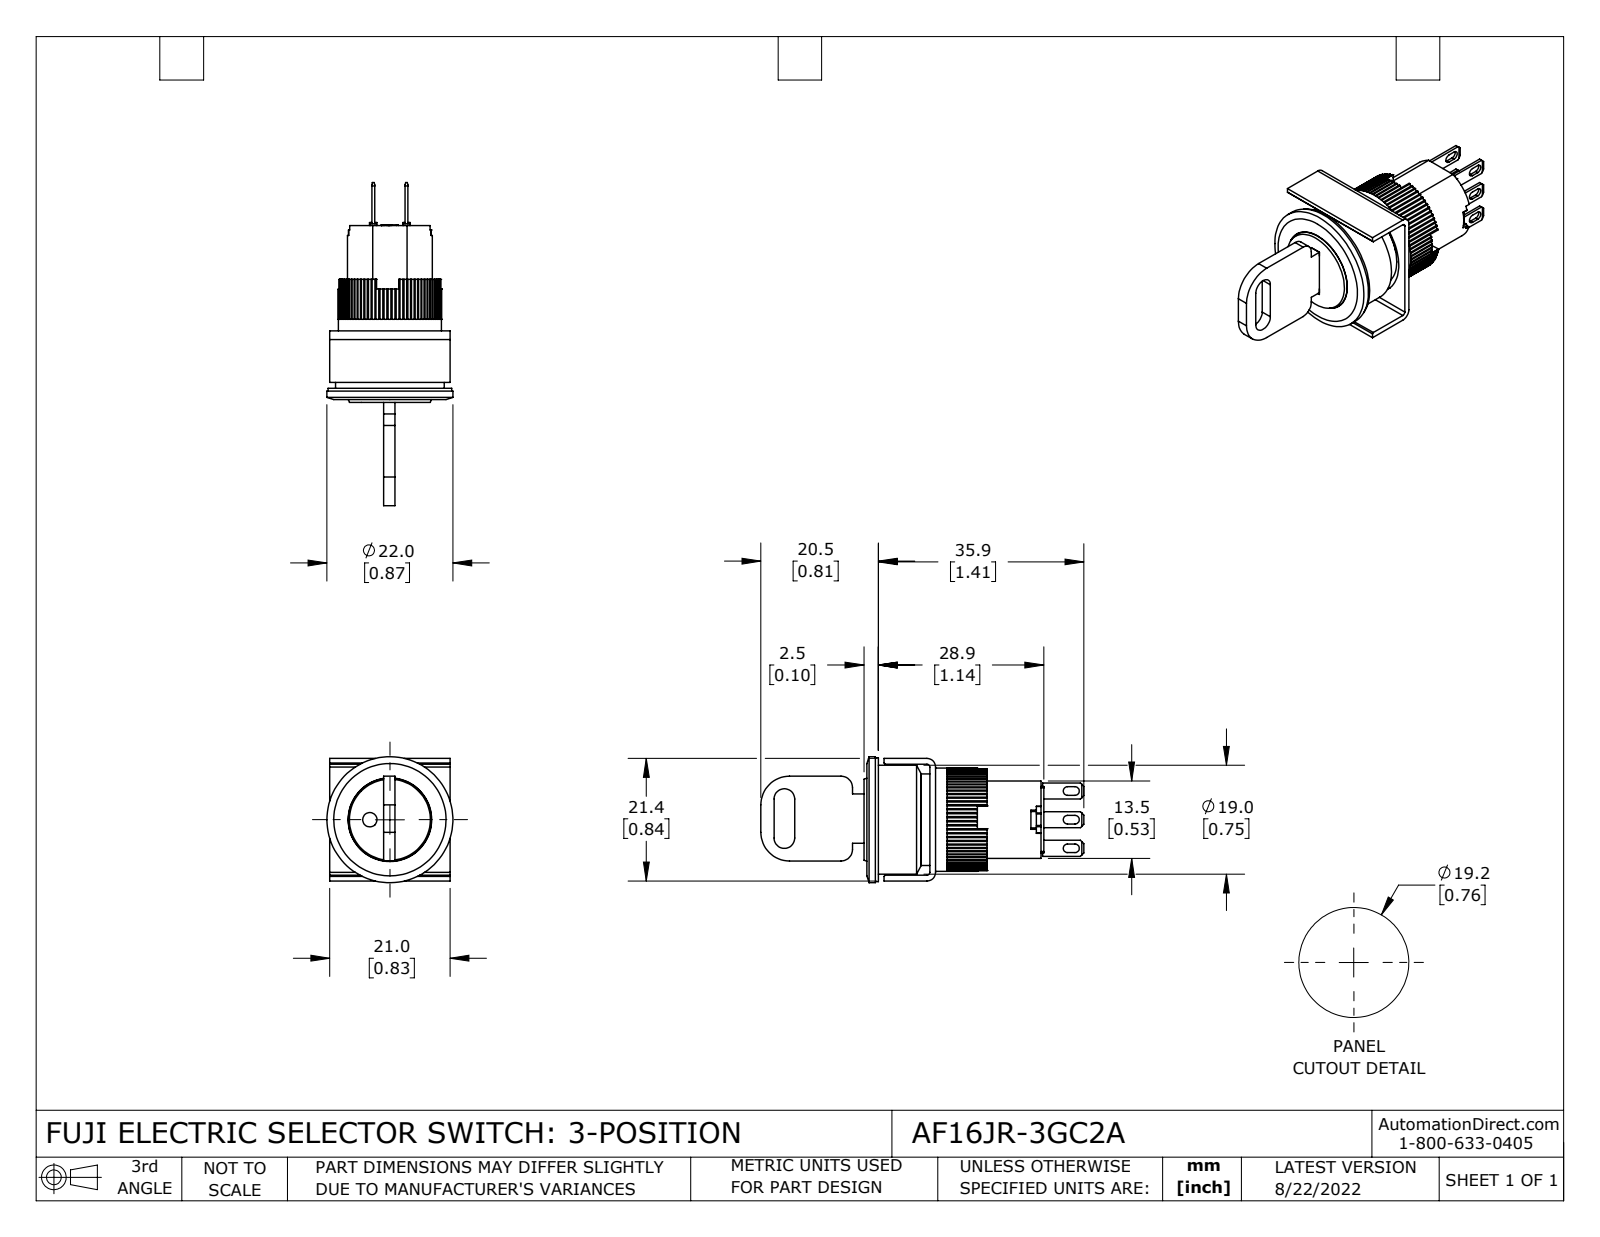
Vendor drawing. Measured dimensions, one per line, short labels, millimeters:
name: AF16JR-3GC2A
written by: SolidWorks 2021 (CONFIG_CONTROL_DESIGN)
unit: mm
bodies: 13 solids, 707 faces (518 planar, 183 cylindrical, 6 other)
size: 56.4 × 22 × 22
volume: 8 110 mm³; area: 7 252 mm²
holes: 1× ⌀1, 1× ⌀2.5, 1× ⌀14.6, 1× ⌀18, 1× ⌀19
bosses: 1× ⌀22, 1× ⌀21.6, 1× ⌀16, 1× ⌀14.8, 1× ⌀14.5
rounds: 80× R0.3, 12× R0.2, 6× R0.8, 2× R0.5, 2× R1.5, 2× R1.8, 2× R2, 2× R5
face distances: 2, 1, 0.5, 9.5, 4.5, 2.5, 10, 20.4, 1.5, 19.4
hole spacings: 3.5
